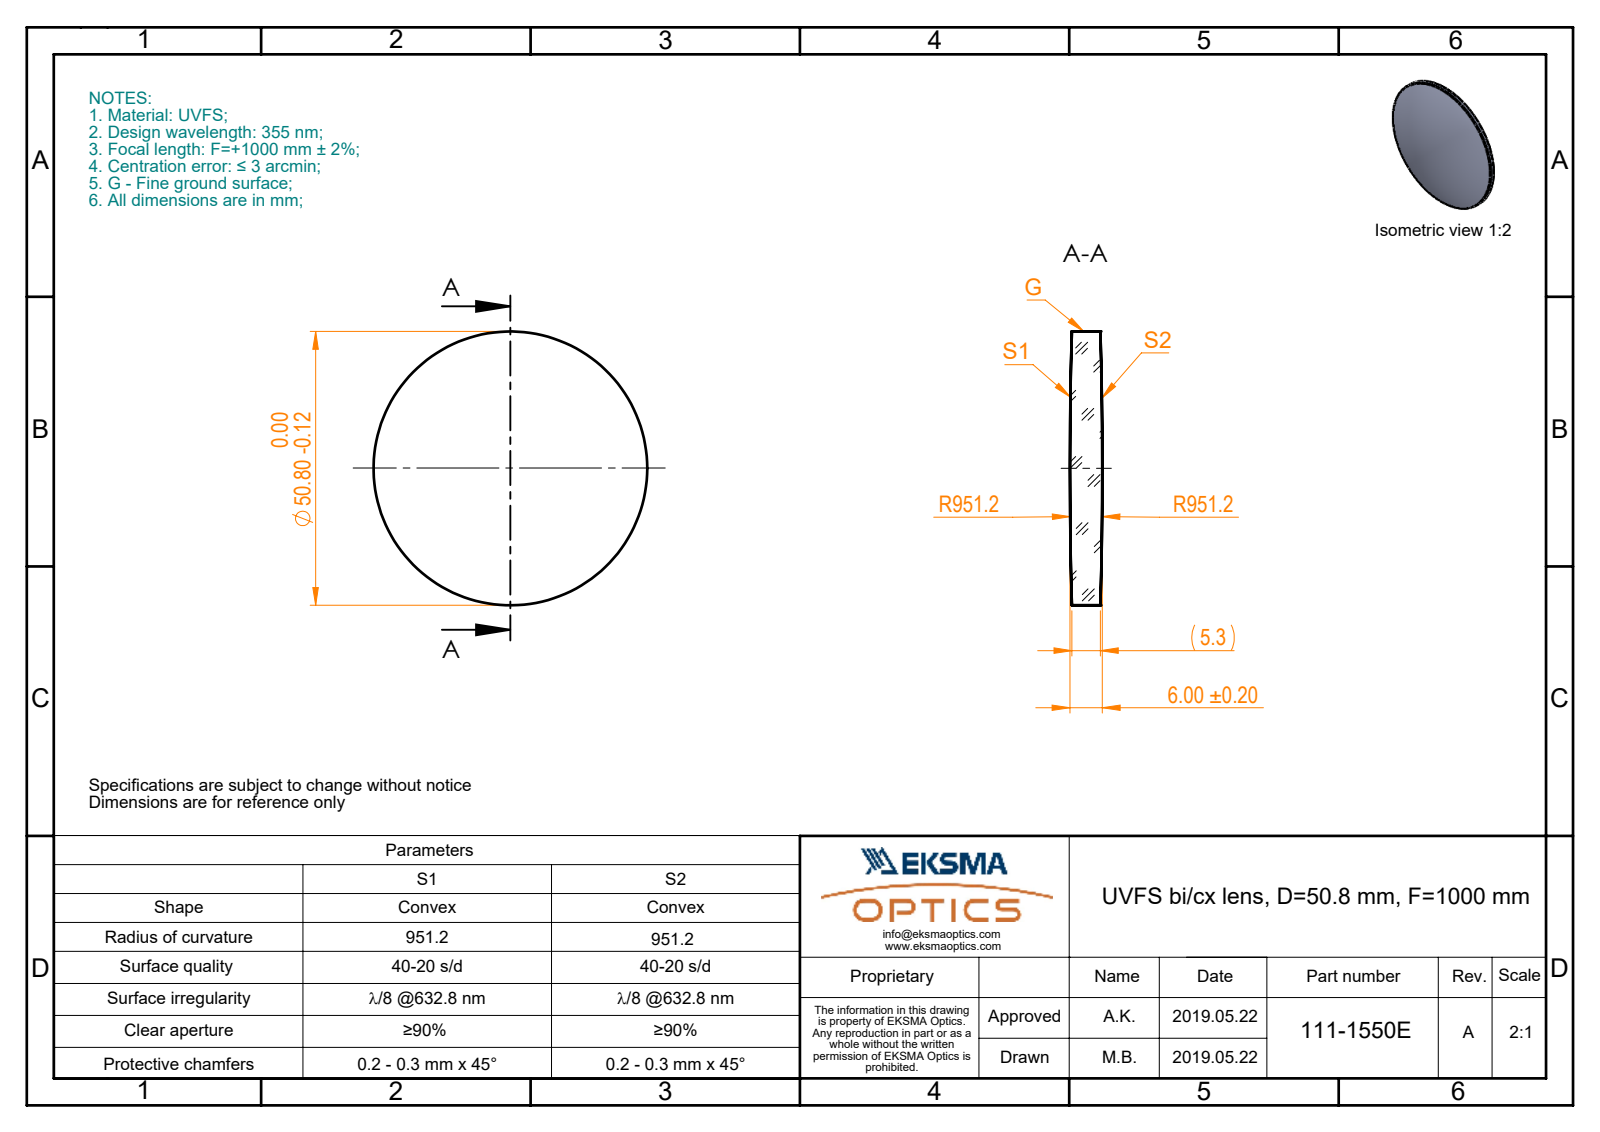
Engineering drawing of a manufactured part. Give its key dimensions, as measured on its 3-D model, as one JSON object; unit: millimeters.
{"part_name": "111-1550E UVFS bi-cx 50.8 F1000", "step_written_by": "SolidWorks 2017 (CONFIG_CONTROL_DESIGN)", "units": "millimeters", "bodies": {"solids": 1, "faces": 6, "planar": 0, "cylindrical": 2, "other": 4}, "overall_size": [50.8, 50.8, 6], "volume_mm3": 11474, "surface_area_mm2": 4904, "round_bosses_or_shafts": [[50.8, 1]]}
